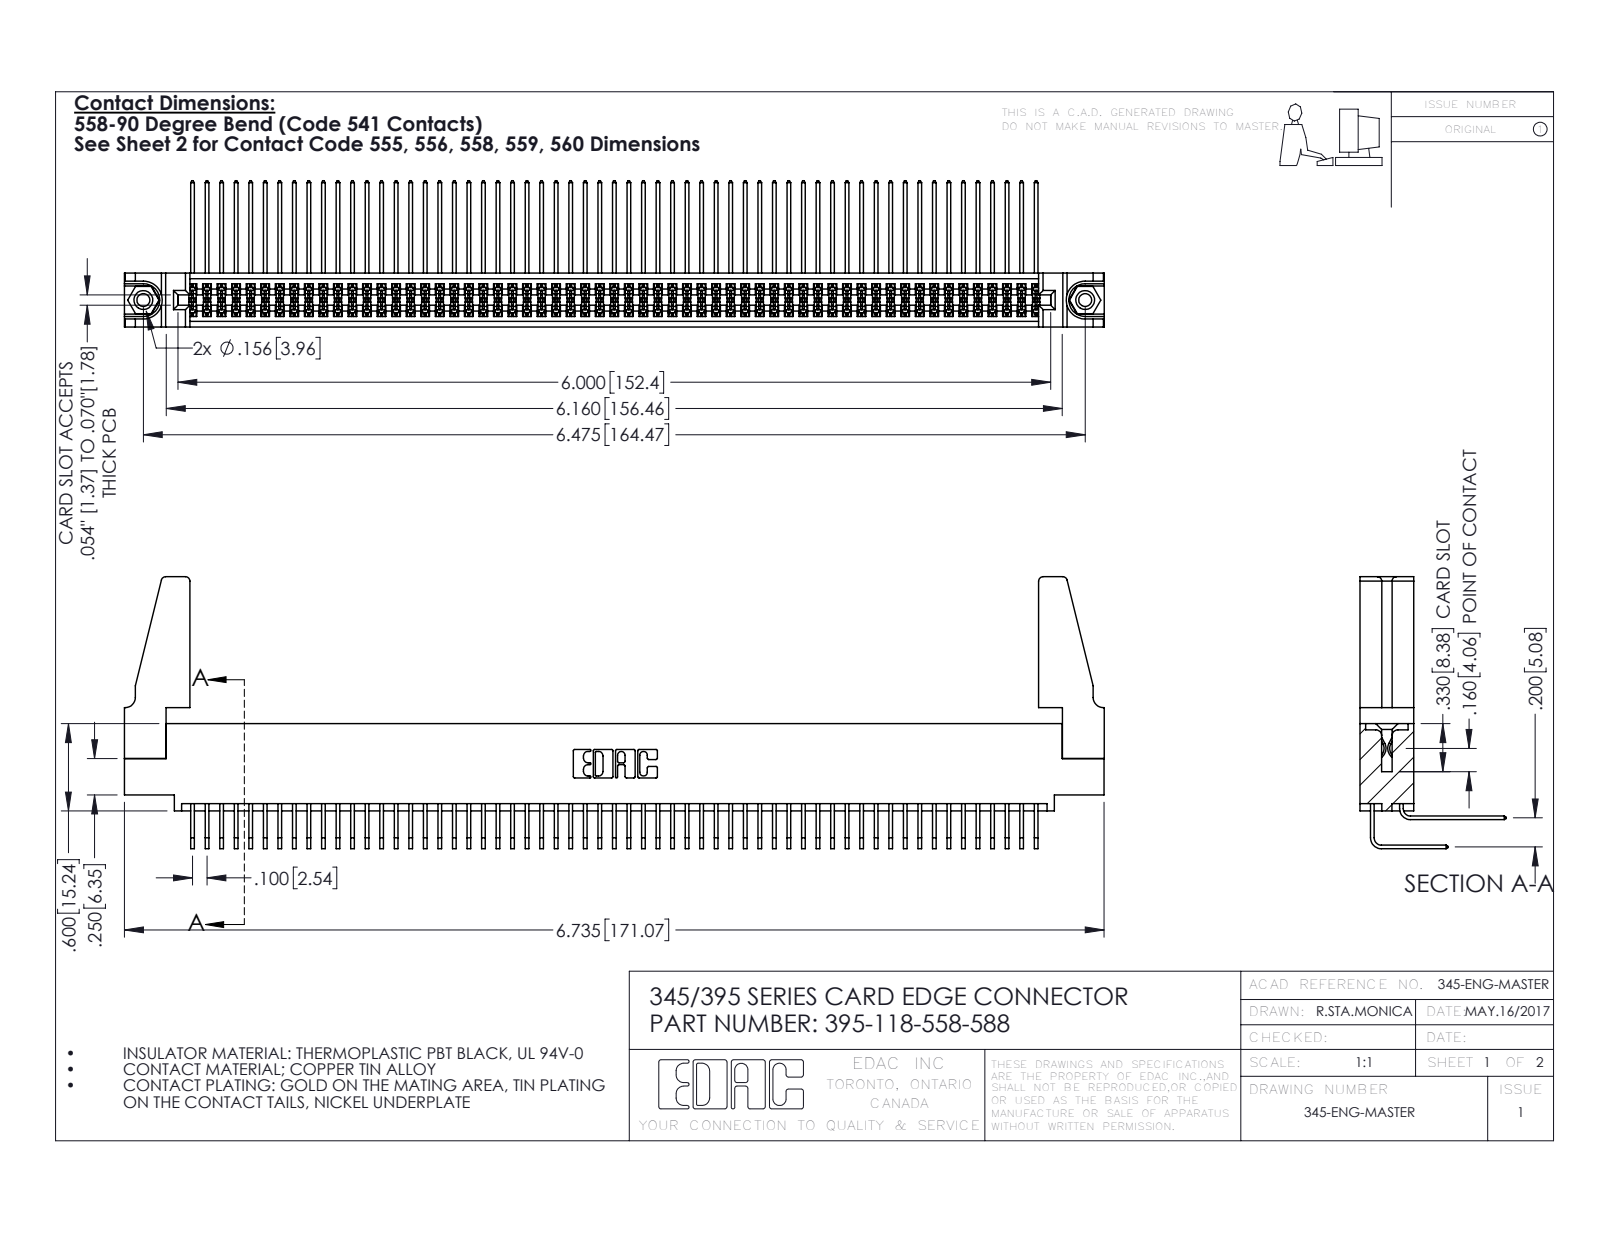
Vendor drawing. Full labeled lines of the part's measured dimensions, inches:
Part name (STEP PRODUCT): 345-220-078_345-220-088; 345-292-001_558 Tail - 2; 345-250-001_345-250-001-102; 345 Part_0.110 Offset - 0.156 Dia-TH (+2 more)
STEP written by: SolidWorks 2016 (CONFIG_CONTROL_DESIGN)
Units: inches
Bodies: 123 solids, 6390 faces (4286 planar, 2088 cylindrical, 16 other)
Overall size (bounding box): 6.736 × 1.869 × 1.005
Volume: 1.259 in³ · Surface area: 50.29 in²
Round holes (diameter × count): ⌀0.089 ×2, ⌀0.125 ×2, ⌀0.156 ×2, ⌀0.064 ×1
Round bosses / shafts (diameter × count): ⌀0.155 ×2
Partial cylindrical surfaces — rounded edges, fillets, slot ends (radius × count): R0.006 ×178, R0.01 ×22, R0.03 ×8, R0.007 ×6, R0.031 ×6, R0.026 ×3, R0.014 ×2, R0.019 ×2
Main face-to-face distances: 0.072, 0.298, 0.2, 0.37, 0.098, 0.272, 0.025, 0.225, 0.025, 0.175
Hole centre spacings: 0.27, 6.239, 6.475
